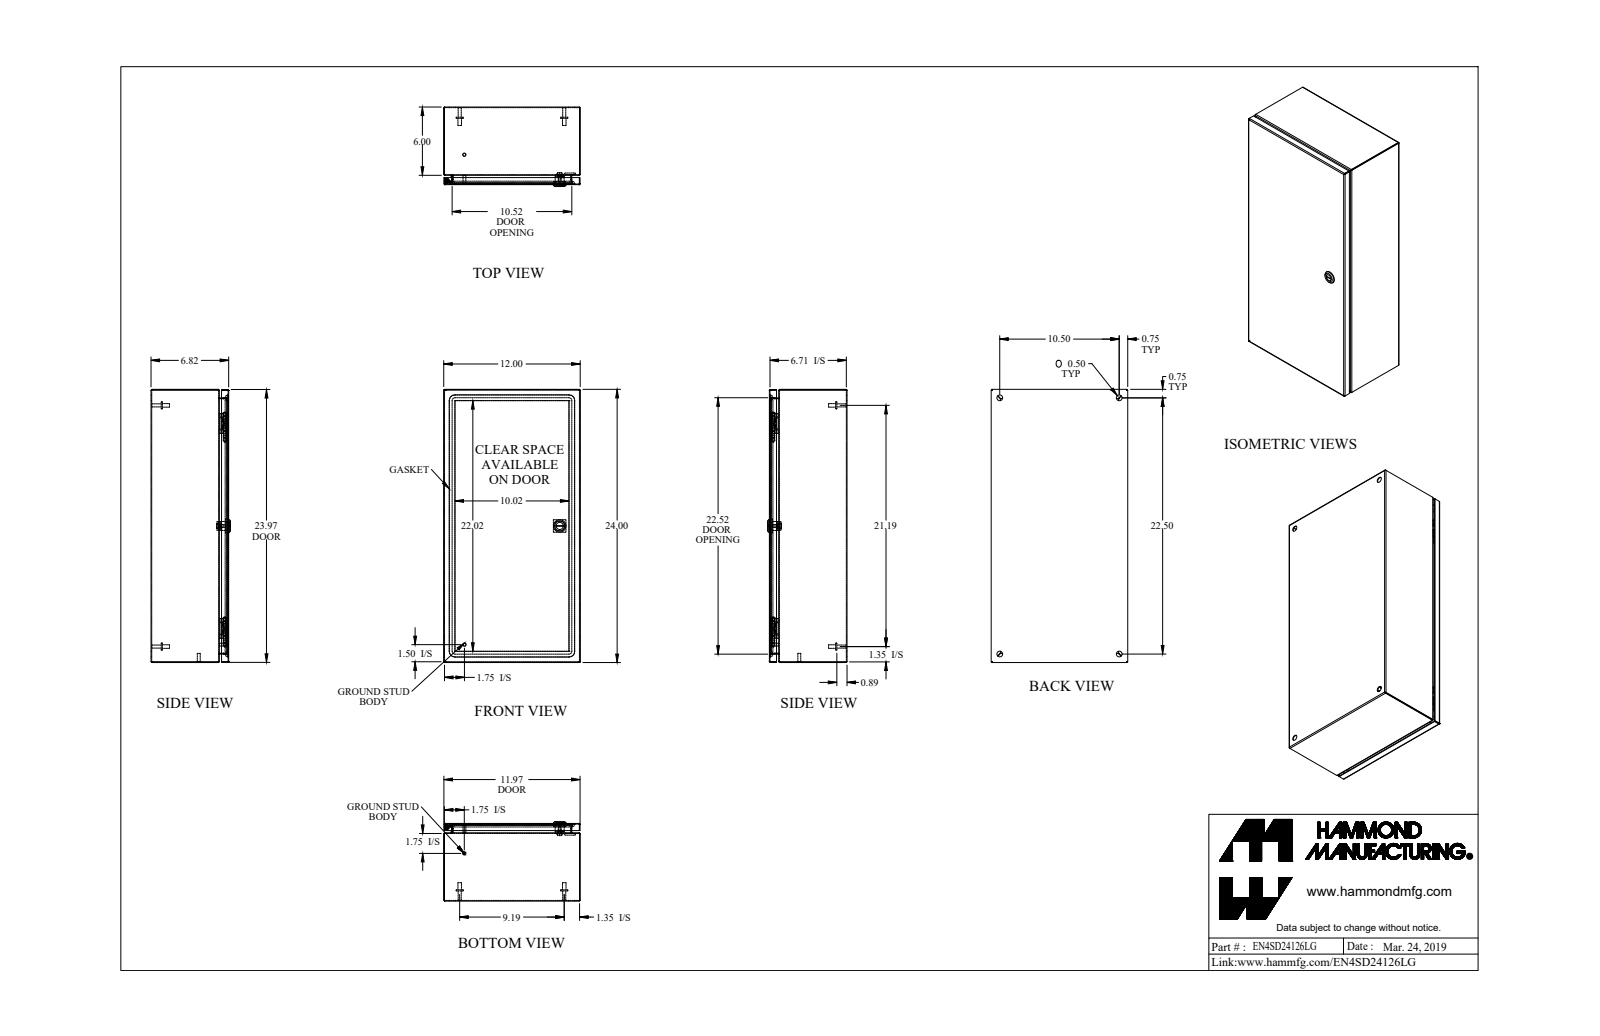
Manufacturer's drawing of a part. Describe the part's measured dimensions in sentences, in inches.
The part is named "EN4SD24126LG_Default". Its 3-D file was written by "SolidWorks 2019 (CONFIG_CONTROL_DESIGN)". It is 21 solids with 634 faces: 285 planar, 213 cylindrical and 136 other. Overall it measures 24 by 12 by 6.982 inches. Its volume is 72.64 cubic inches and its surface area 2 457 square inches. Round holes: 4 of diameter 0.5, 1 of diameter 0.172, 1 of diameter 0.232, 1 of diameter 0.24, 1 of diameter 0.242, 1 of diameter 0.625, 1 of diameter 0.785. Round bosses or shafts: 4 of diameter 0.625, 4 of diameter 0.313, 4 of diameter 0.27, 2 of diameter 0.281, 2 of diameter 0.25, 1 of diameter 1.1, 1 of diameter 0.525, 1 of diameter 0.455. Partial cylindrical surfaces (rounded edges, fillets, slot ends): 21 of radius 0.029, 21 of radius 0.086, 16 of radius 0.25, 8 of radius 19, 4 of radius 0.006, 4 of radius 0.062, 4 of radius 0.499, 2 of radius 0.125. The main face-to-face distances are 0.057, 6.765, 6.708, 6.822, 11.943, 11.886, 12, 23.943, 0.822, 5.943. The hole center spacings are 10.5, 22.5, 24.83, 11.299, 11.3, 14.686, 14.687.
